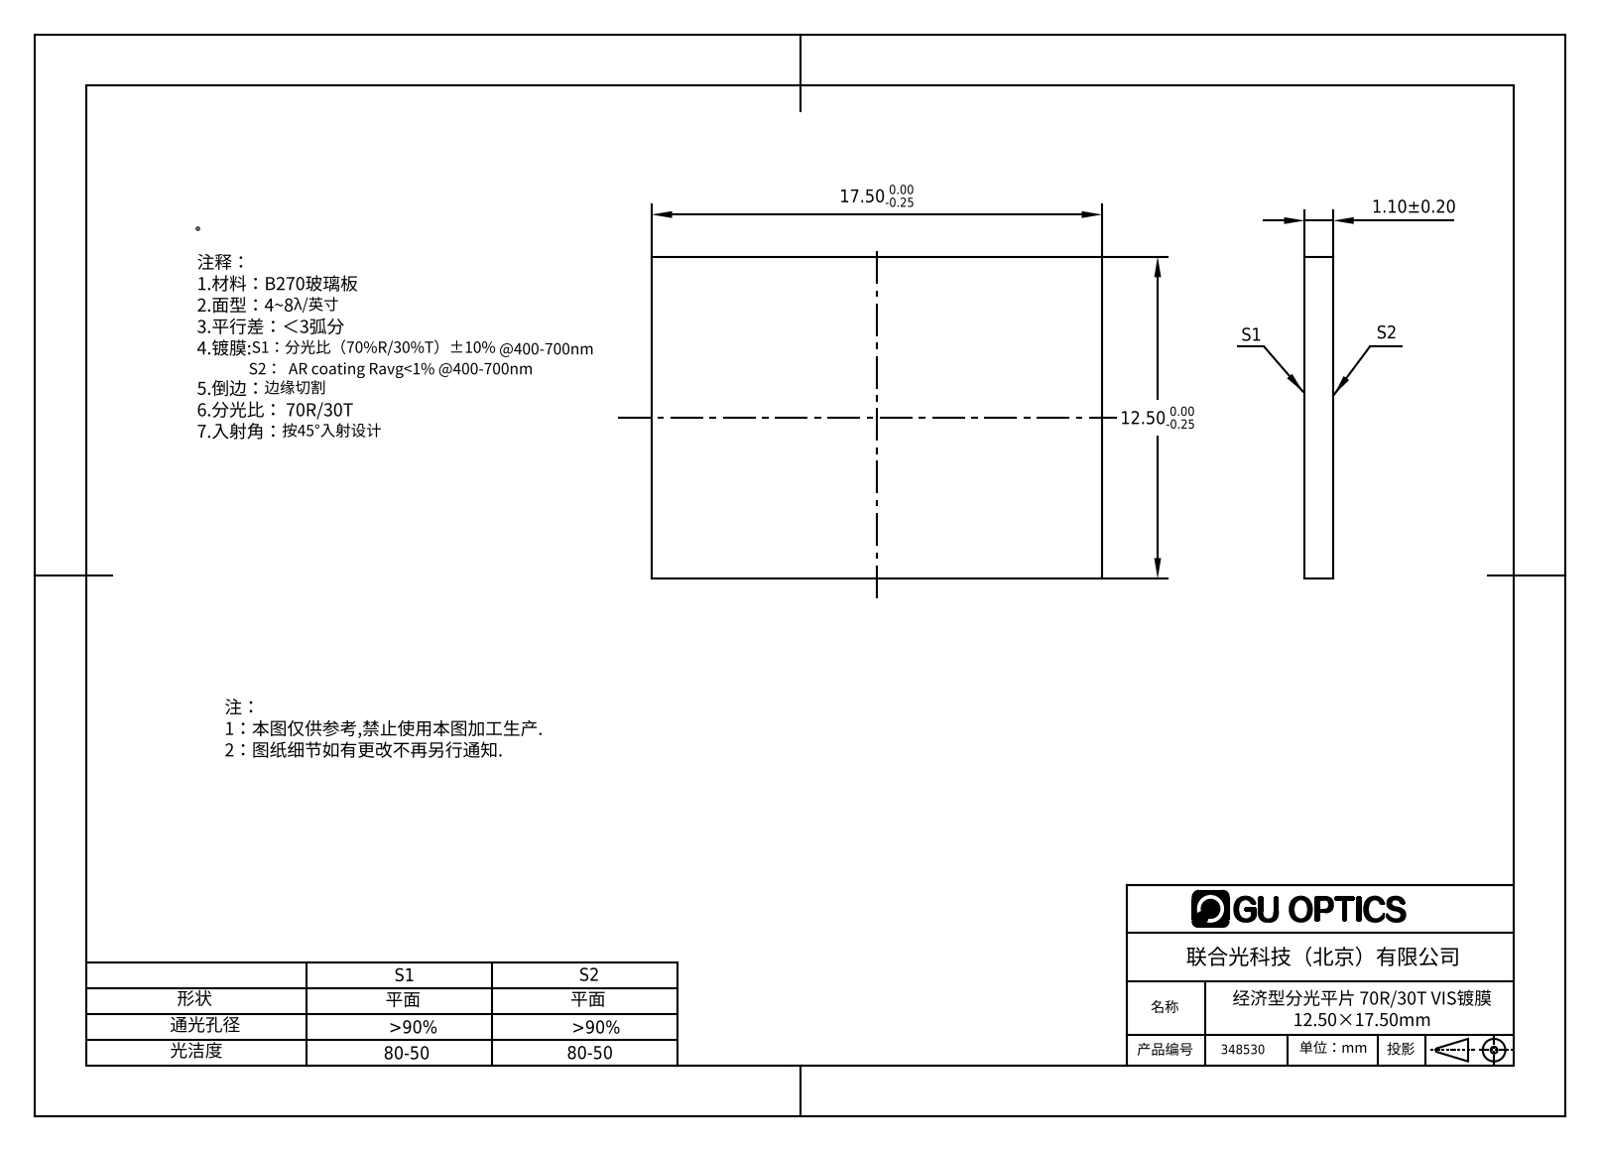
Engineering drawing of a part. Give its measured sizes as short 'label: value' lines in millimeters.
name: 348502
written by: SolidWorks 2016 (CONFIG_CONTROL_DESIGN)
unit: mm
bodies: 1 solid, 6 faces (6 planar, 0 cylindrical, 0 other)
size: 17.5 × 12.5 × 1.1
volume: 241 mm³; area: 504 mm²
face distances: 1.1, 12.5, 17.5
